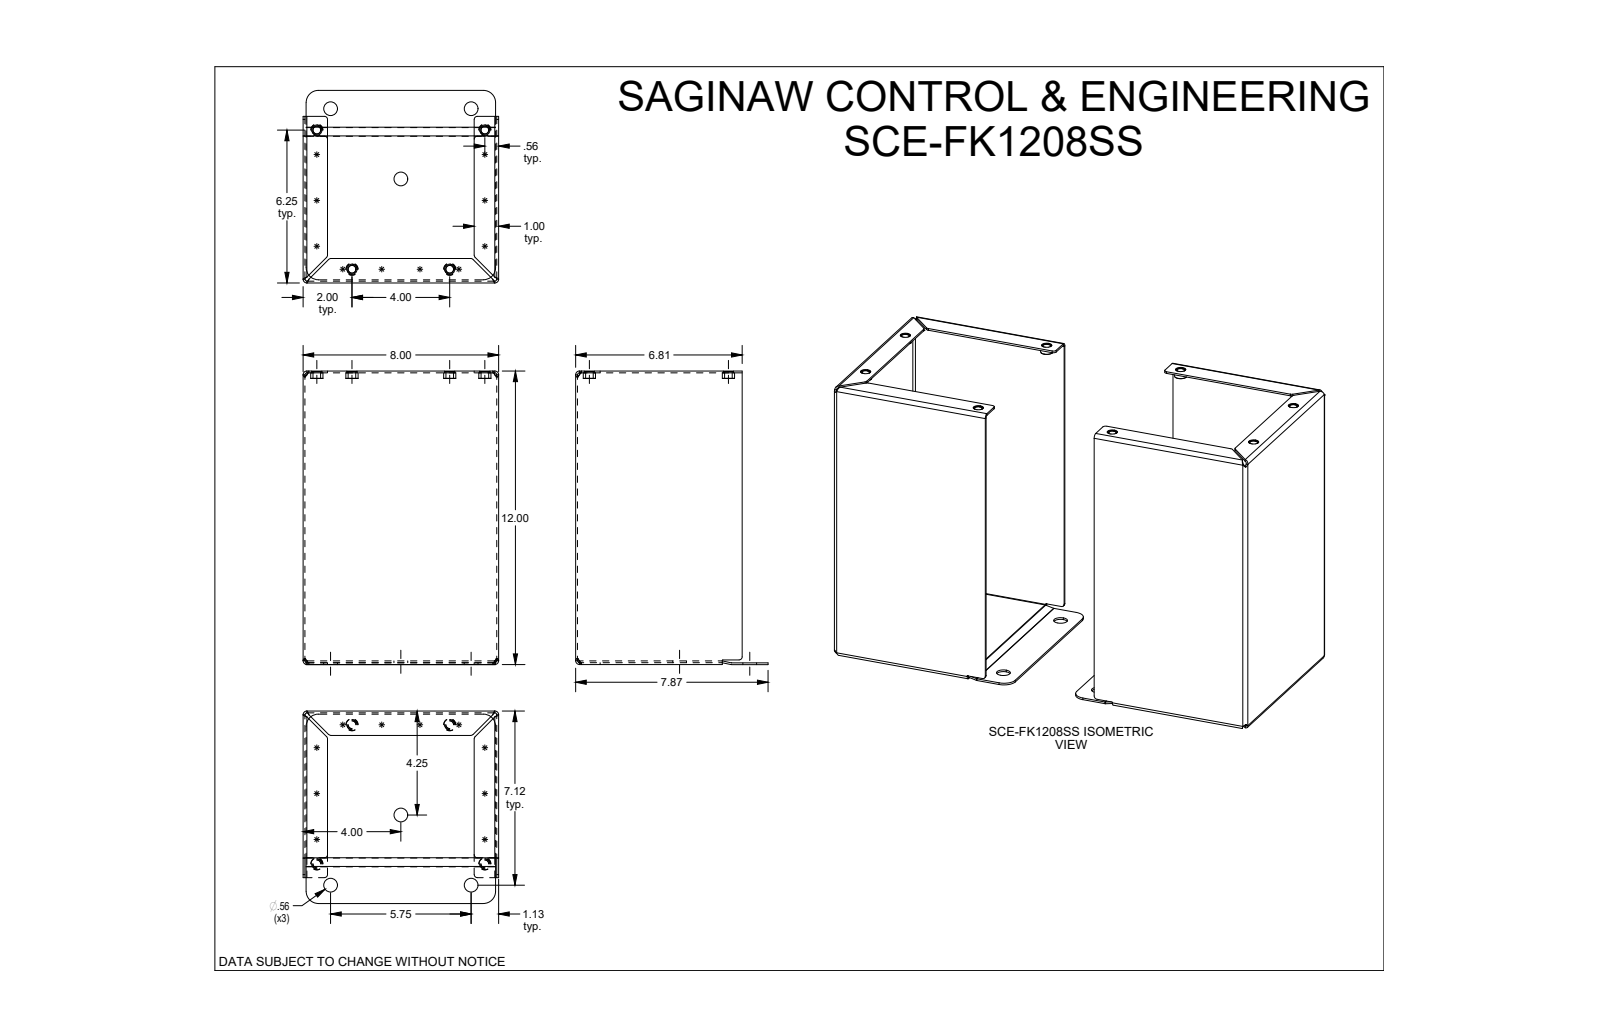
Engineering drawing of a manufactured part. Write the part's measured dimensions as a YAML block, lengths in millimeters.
part_name: "SCE-FK1208SS"
step_written_by: "SolidWorks 2019 (CONFIG_CONTROL_DESIGN)"
units: millimeters
bodies: {solids: 12, faces: 294, planar: 120, cylindrical: 118, other: 56}
overall_size: [469.9, 304.9, 203.2]
volume: 855600
surface_area: 909700
round_holes:
  - {diameter: 7.9, count: 8}
  - {diameter: 10.5, count: 8}
  - {diameter: 14.3, count: 6}
round_bosses_or_shafts:
  - {diameter: 12.7, count: 8}
  - {diameter: 10.5, count: 8}
partial_cylinders:
  - {radius: 3.2, count: 19}
  - {radius: 2, count: 12}
  - {radius: 3.9, count: 12}
  - {radius: 12.7, count: 8}
  - {radius: 3.5, count: 4}
  - {radius: 0.5, count: 2}
  - {radius: 1.6, count: 2}
  - {radius: 1.6, count: 2}
face_to_face_distances: [1.9, 1.9, 201.3, 468, 203.2, 469.9, 466.1, 199.4, 199.4, 201.3]
hole_center_spacings: [101, 106.6, 131, 149, 168.1, 195.1, 199.9, 221.1]
